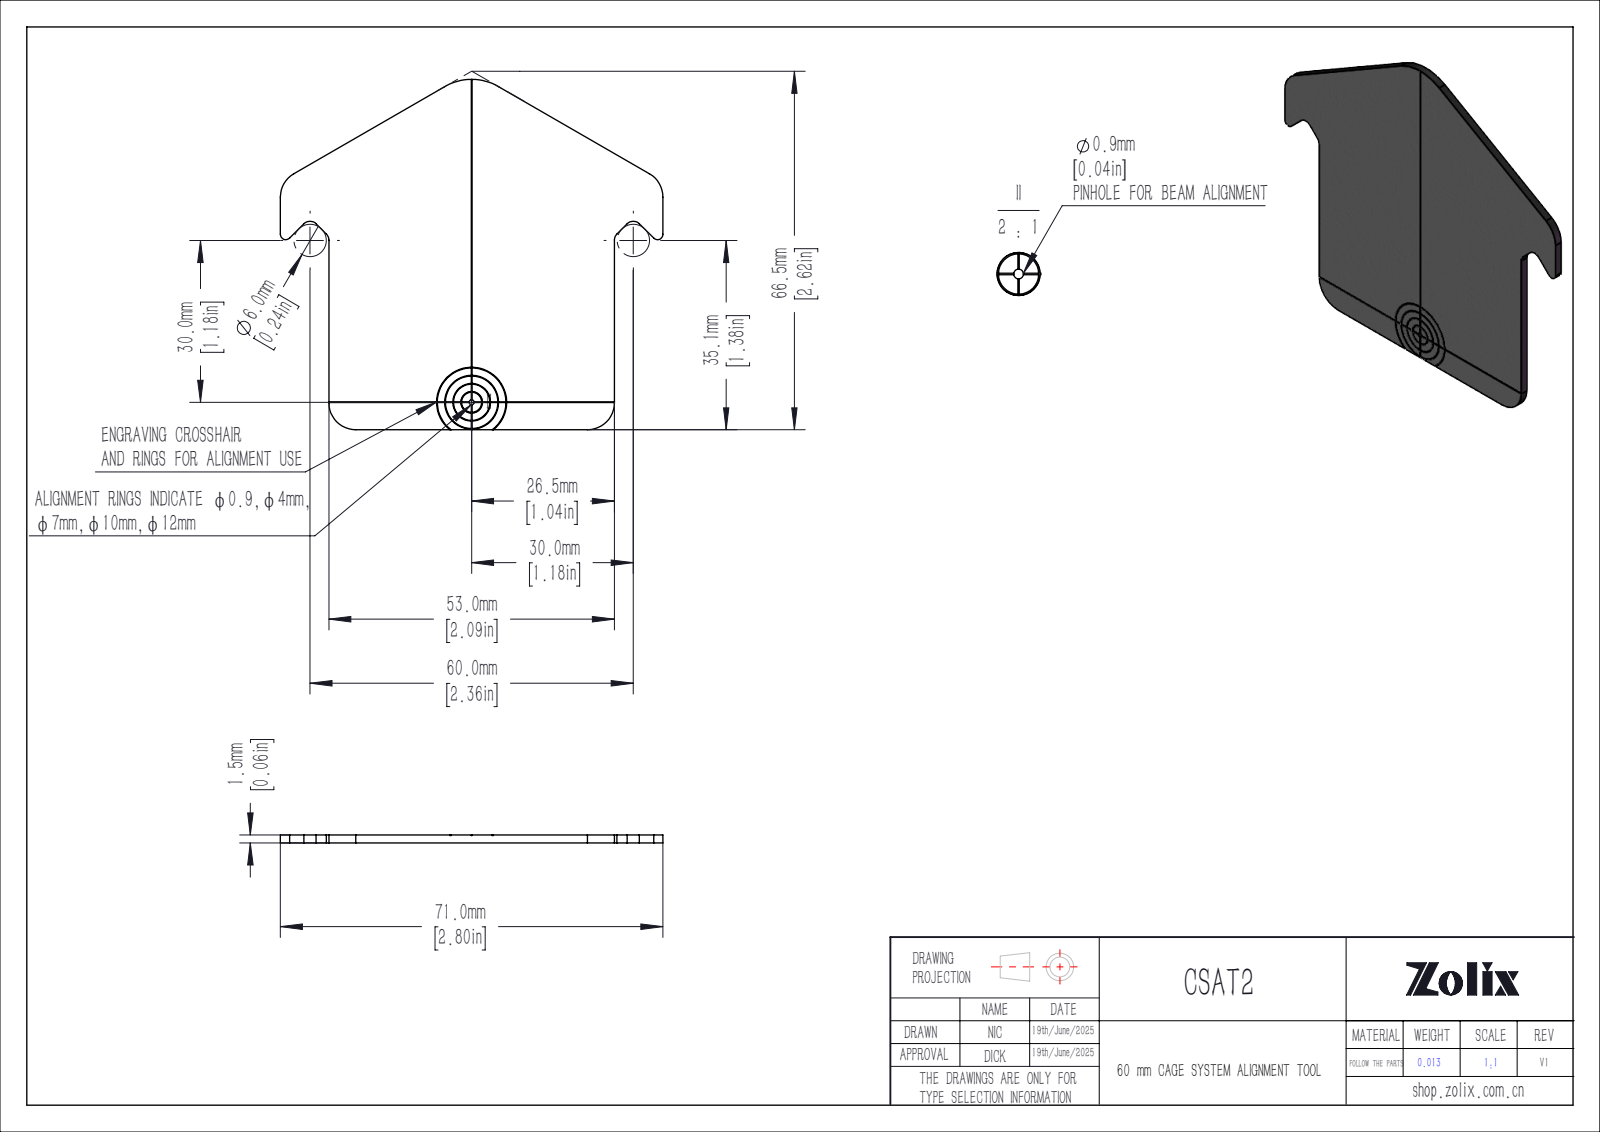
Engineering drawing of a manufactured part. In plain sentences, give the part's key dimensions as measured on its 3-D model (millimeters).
The part is named "CSAT2". Its 3-D file was written by "SolidWorks 2020 (CONFIG_CONTROL_DESIGN)". It is 1 solid with 361 faces: 268 planar, 48 cylindrical and 45 other. Overall it measures 71 by 65 by 1.5 millimeters. Its volume is 4 962 cubic millimeters and its surface area 7 048 square millimeters. Round holes: 1 of diameter 0.9, 1 of diameter 4, 1 of diameter 7, 1 of diameter 10. Round bosses or shafts: 1 of diameter 9.74, 1 of diameter 6.74, 1 of diameter 3.74. Partial cylindrical surfaces (rounded edges, fillets, slot ends): 4 of radius 5, 2 of radius 1, 2 of radius 1.6, 2 of radius 1.6, 1 of radius 6.37, 1 of radius 6.5, 1 of radius 10. The main face-to-face distances are 1.5, 53, 1.37, 9, 62, 1.48, 71, 35.43, 35.56, 26.43.
